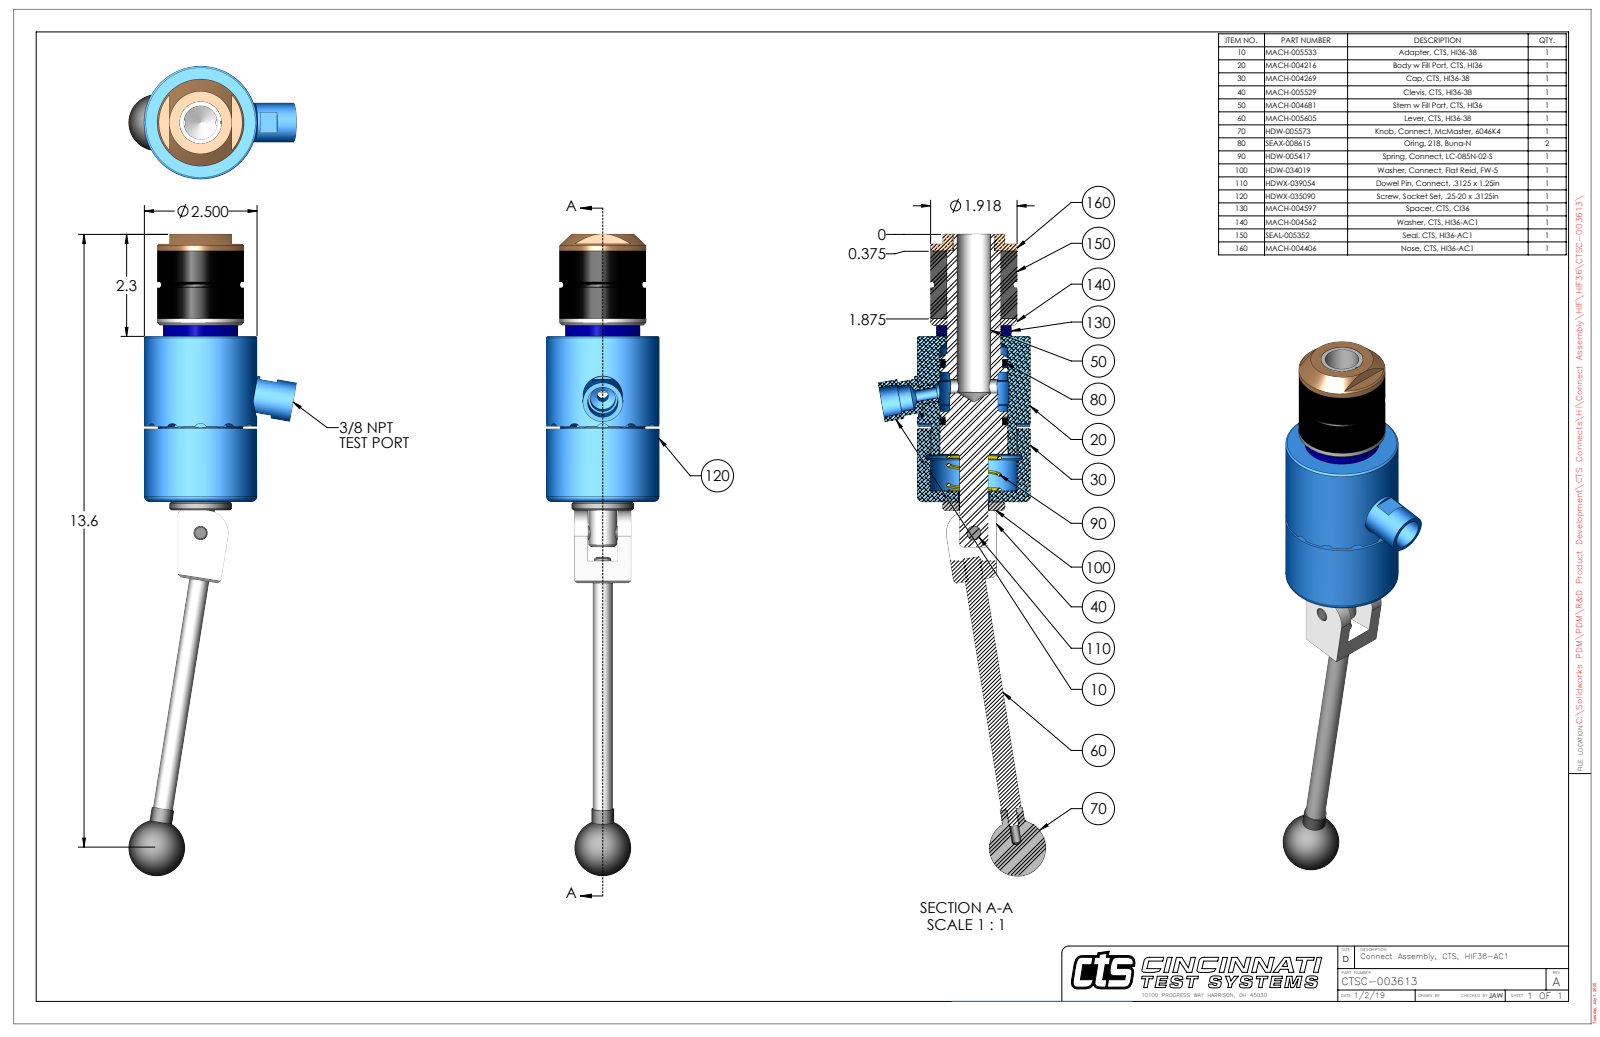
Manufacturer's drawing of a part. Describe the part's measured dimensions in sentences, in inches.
The part is named "CTSC-003613". Its 3-D file was written by "SolidWorks 2023 (AUTOMOTIVE_DESIGN)". It is 10 solids with 307 faces: 109 planar, 127 cylindrical and 71 other. Overall it measures 14.215 by 3.716 by 2.5 inches. Its volume is 26.16 cubic inches and its surface area 131.8 square inches. Round holes: 2 of diameter 0.201, 1 of diameter 0.15, 1 of diameter 0.25, 1 of diameter 0.311, 1 of diameter 0.312, 1 of diameter 0.313, 1 of diameter 0.314, 1 of diameter 0.562, 1 of diameter 0.656, 1 of diameter 0.696, 1 of diameter 0.75, 1 of diameter 0.922. Round bosses or shafts: 1 of diameter 2.5, 1 of diameter 1.918, 1 of diameter 1.875, 1 of diameter 1.656, 1 of diameter 1.38, 1 of diameter 1.186, 1 of diameter 1, 1 of diameter 0.904. Partial cylindrical surfaces (rounded edges, fillets, slot ends): 12 of radius 0.12, 2 of radius 0.029, 1 of radius 0.19, 1 of radius 0.195, 1 of radius 0.447, 1 of radius 0.47, 1 of radius 0.5, 1 of radius 1.176. The main face-to-face distances are 3.668, 5.555, 1.887, 4.055, 0.387, 1.5, 3.905, 0.237, 0.15, 1.65. The hole center spacings are 0.74, 2.118, 2.858.
